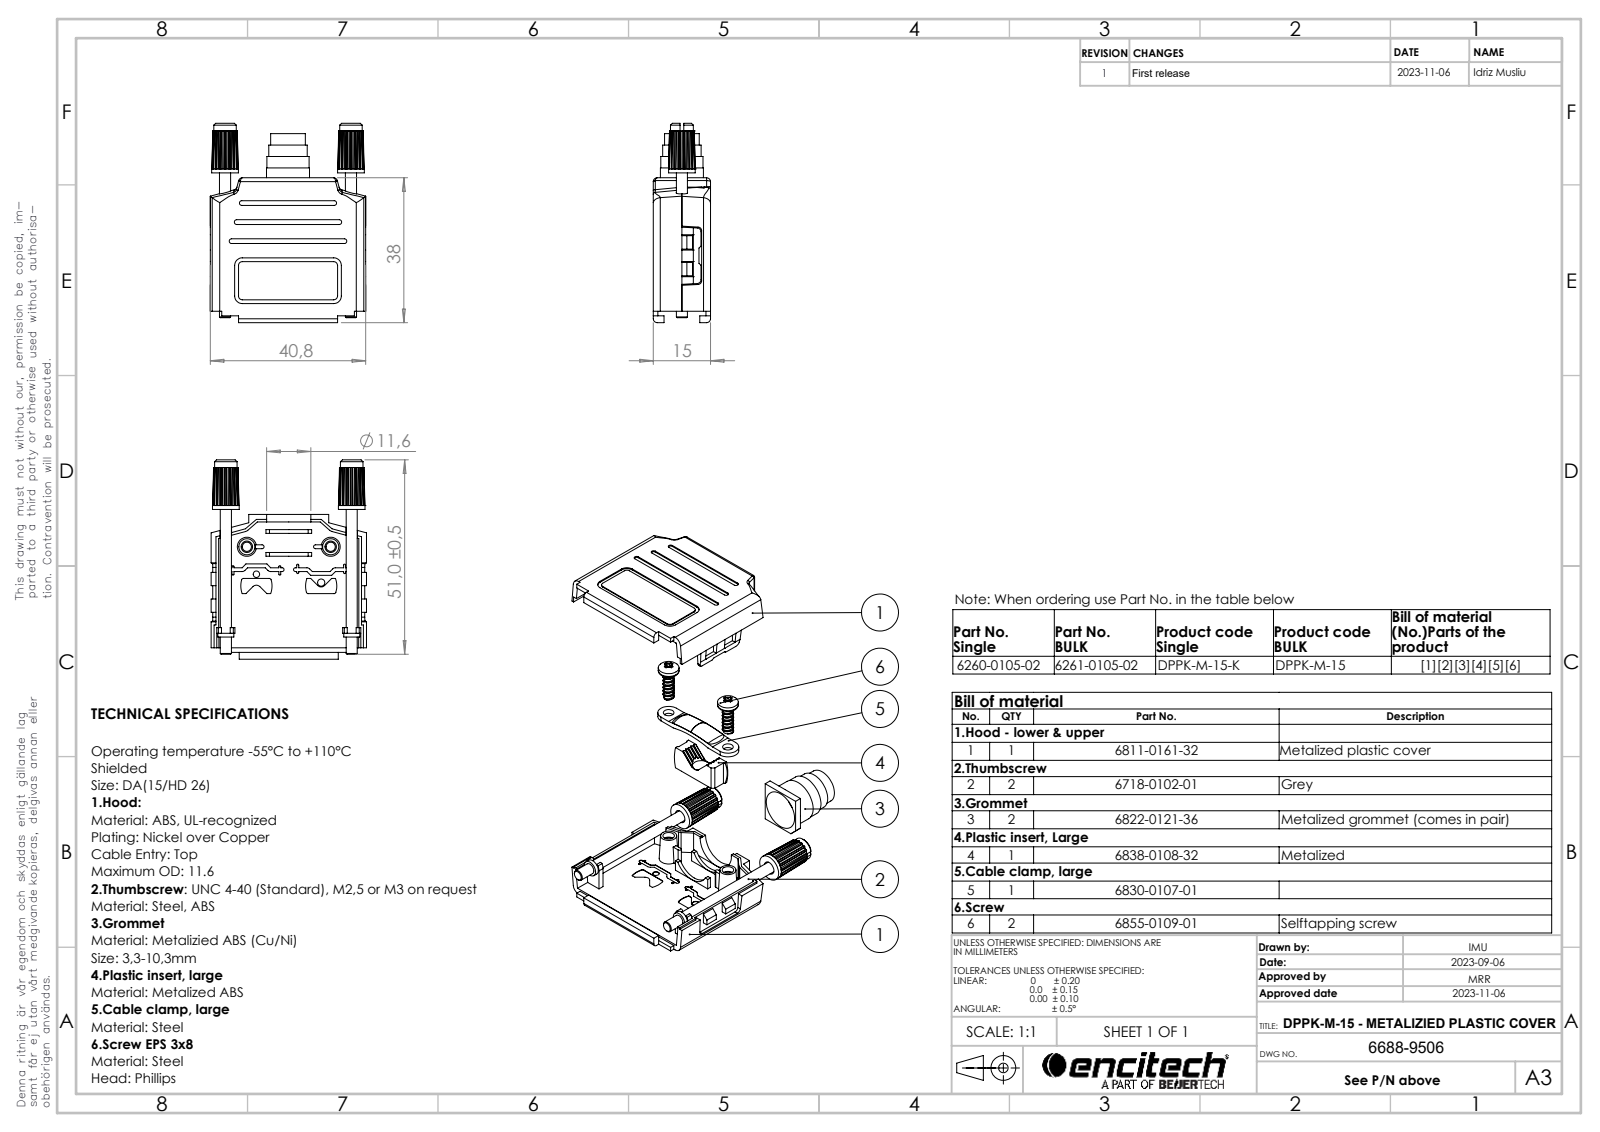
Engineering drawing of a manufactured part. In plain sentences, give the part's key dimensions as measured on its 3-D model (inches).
The part is named "6838-0108-01; 6718-0102-01; 6822-0121 part 1; 6855-0109-01 (+4 more)". Its 3-D file was written by "SolidWorks 2021 (AUTOMOTIVE_DESIGN)". It is 11 solids with 1056 faces: 726 planar, 231 cylindrical and 99 other. Overall it measures 2.059 by 1.606 by 0.591 inches. Its volume is 0.552 cubic inches and its surface area 21.48 square inches. Round holes: 4 of diameter 0.118, 2 of diameter 0.094, 2 of diameter 0.11, 1 of diameter 0.067, 1 of diameter 0.075, 1 of diameter 0.128, 1 of diameter 0.181, 1 of diameter 0.207, 1 of diameter 0.295, 1 of diameter 0.335, 1 of diameter 0.374, 1 of diameter 0.413. Round bosses or shafts: 2 of diameter 0.276, 2 of diameter 0.236, 2 of diameter 0.215, 2 of diameter 0.165, 2 of diameter 0.114, 1 of diameter 0.445, 1 of diameter 0.437, 1 of diameter 0.398. Partial cylindrical surfaces (rounded edges, fillets, slot ends): 30 of radius 0.039, 14 of radius 0.02, 12 of radius 0.01, 9 of radius 0.024, 6 of radius 0.236, 5 of radius 0.079, 4 of radius 0.017, 3 of radius 0.049. The main face-to-face distances are 0.524, 0.067, 0.063, 0.457, 0.591, 0.047, 0.291, 0.587, 0.52, 0.051. The hole center spacings are 0.65, 0.055, 0.11, 0.3, 0.33, 0.383, 0.406, 0.433.
